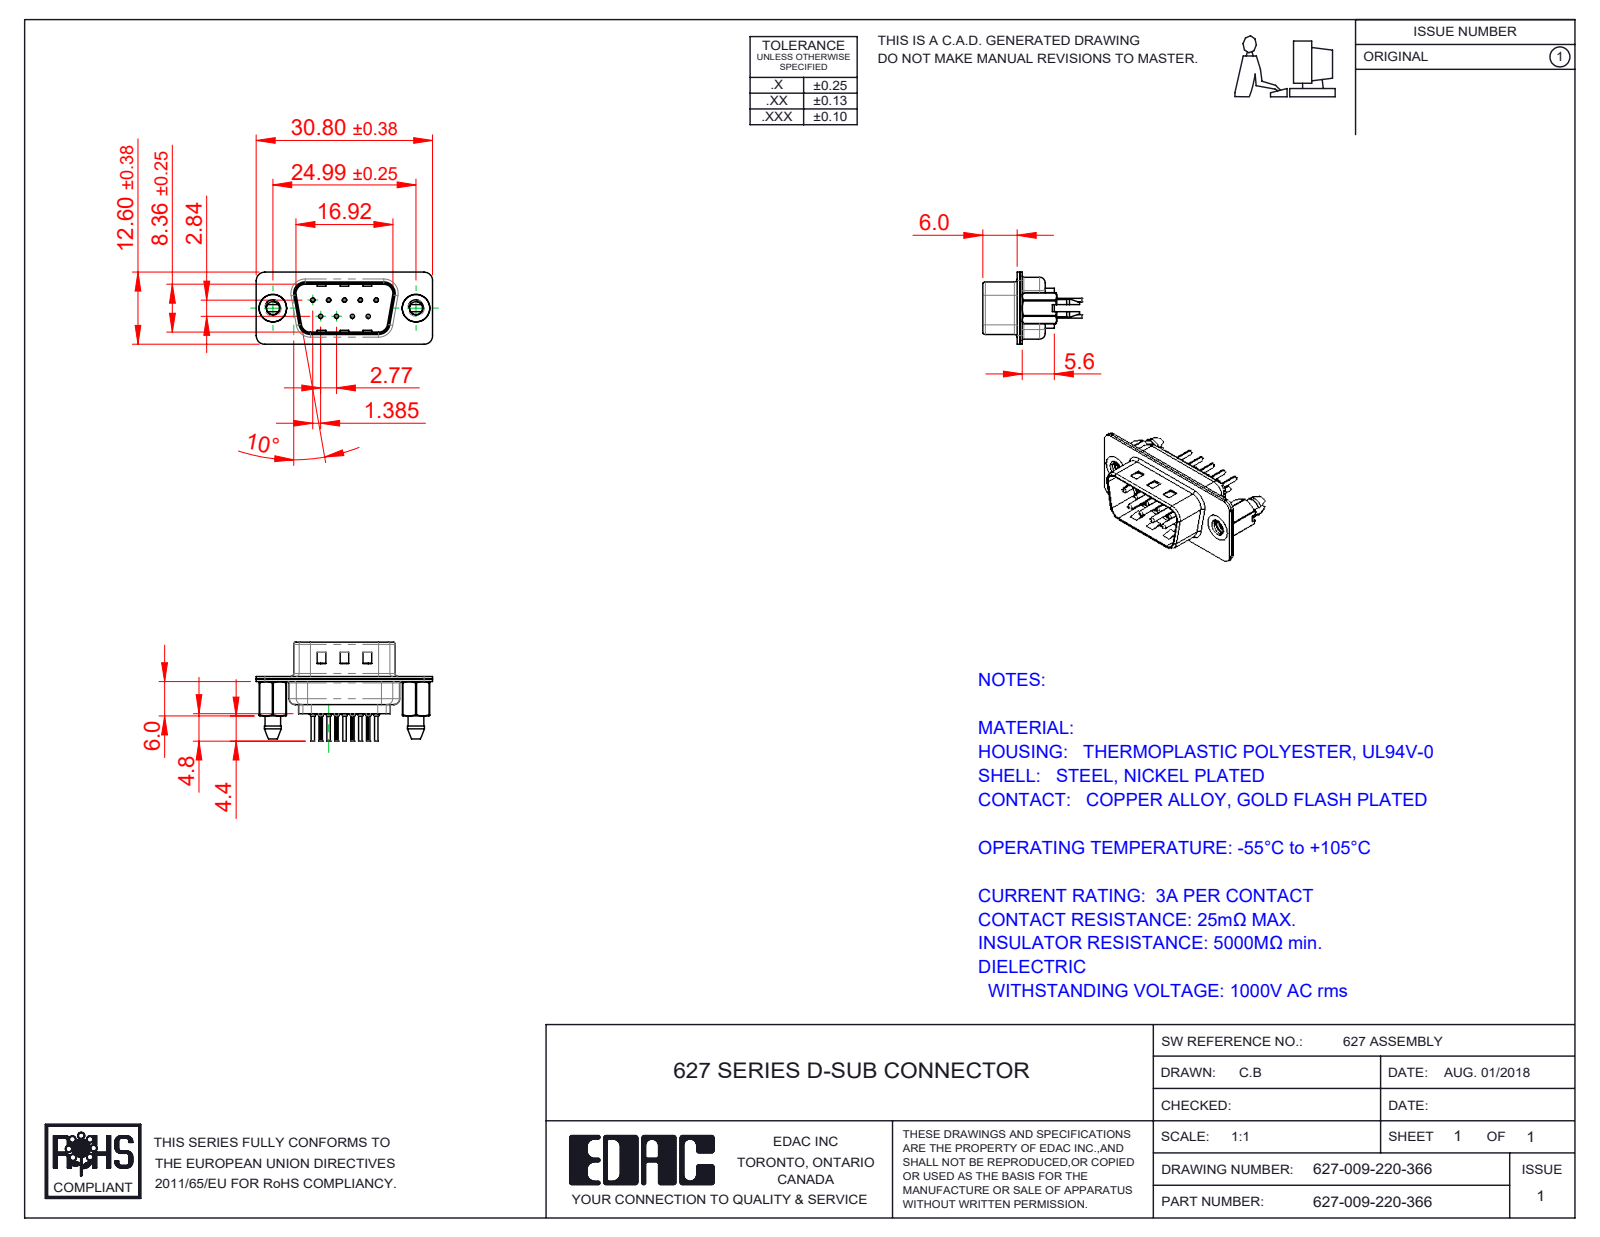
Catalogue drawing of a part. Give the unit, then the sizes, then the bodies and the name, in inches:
Units: inches
Overall size (bounding box): 1.213 × 0.681 × 0.496
Round holes (diameter × count): ⌀0.008 ×9, ⌀0.014 ×9, ⌀0.043 ×9, ⌀0.063 ×9, ⌀0.089 ×2, ⌀0.157 ×2, ⌀0.189 ×2
Round bosses / shafts (diameter × count): ⌀0.079 ×9, ⌀0.059 ×9, ⌀0.03 ×9, ⌀0.024 ×9, ⌀0.193 ×2
Partial cylindrical surfaces — rounded edges, fillets, slot ends (radius × count): R0.059 ×20, R0.004 ×18, R0.079 ×12, R0.063 ×10, R0.02 ×8, R0.01 ×4, R0.024 ×4, R0.026 ×4
Main face-to-face distances: 0.018, 0.016, 0.035, 0.032, 0.377, 0.055, 0.345, 0.256, 0.02, 0.059
Hole centre spacings: 0.124, 0.109, 0.218, 0.198, 0.198, 0.327, 0.294, 0.295
Volume: 0.087 in³ · Surface area: 6.55 in²
Bodies: 14 solids, 1260 faces (355 planar, 494 cylindrical, 411 other)
Part name (STEP PRODUCT): 627 Shell Rear_09 Contacts; 627 Shell Front_09 Contacts; 627 Housing_09 LP; 627-009-220-066 (+3 more)
STEP written by: SolidWorks 2020 (CONFIG_CONTROL_DESIGN)
